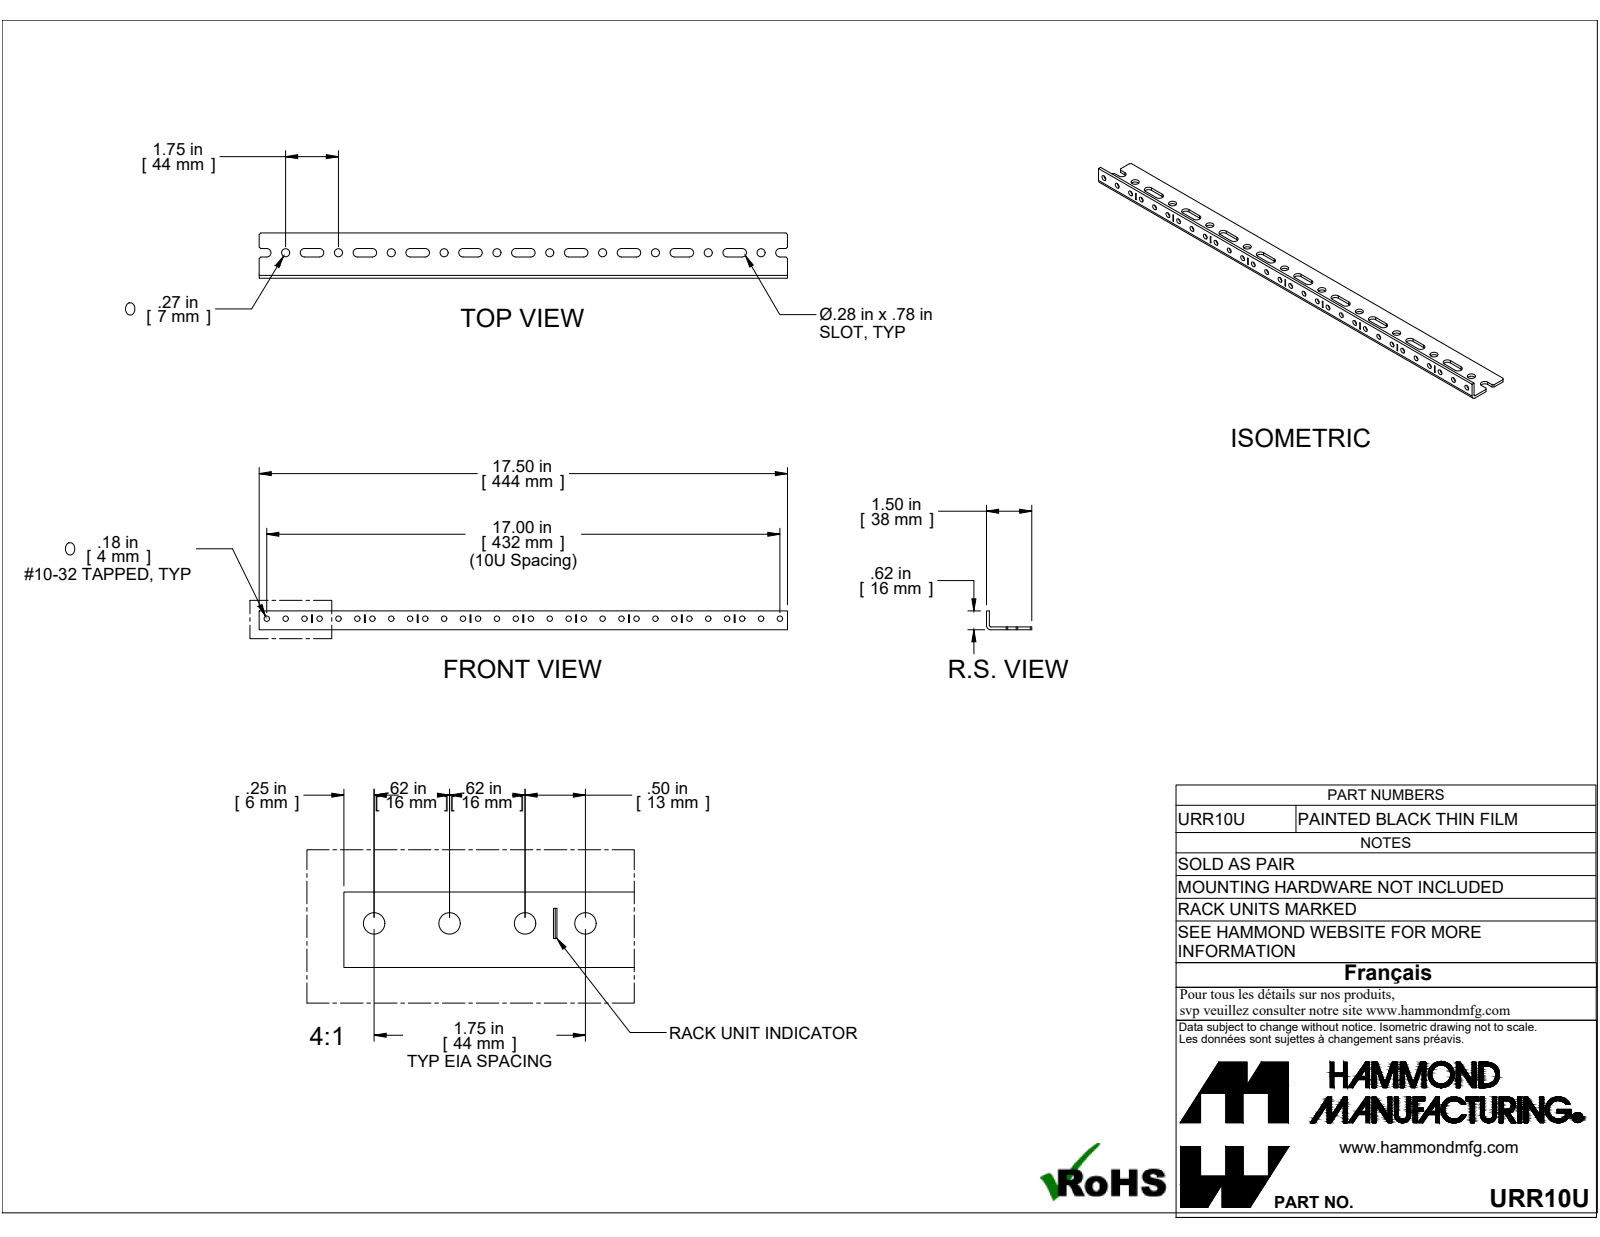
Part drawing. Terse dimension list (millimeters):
name: COM57213-10
written by: ST-DEVELOPER v16.7 (AUTOMOTIVE_DESIGN)
unit: mm
bodies: 1 solid, 136 faces (74 planar, 62 cylindrical, 0 other)
size: 444.5 × 38.1 × 15.88
volume: 48 996 mm³; area: 45 699 mm²
holes: 30× ⌀4.5, 10× ⌀6.76
rounds: 20× R3.57, 1× R1.22, 1× R3.63
face distances: 2.41, 15.88, 13.47, 38.1, 35.69, 17.84, 24.98, 15.43, 22.57, 7.14
hole spacings: 44.45, 88.9, 177.8, 133.35, 266.7, 15.87, 15.88, 28.58
